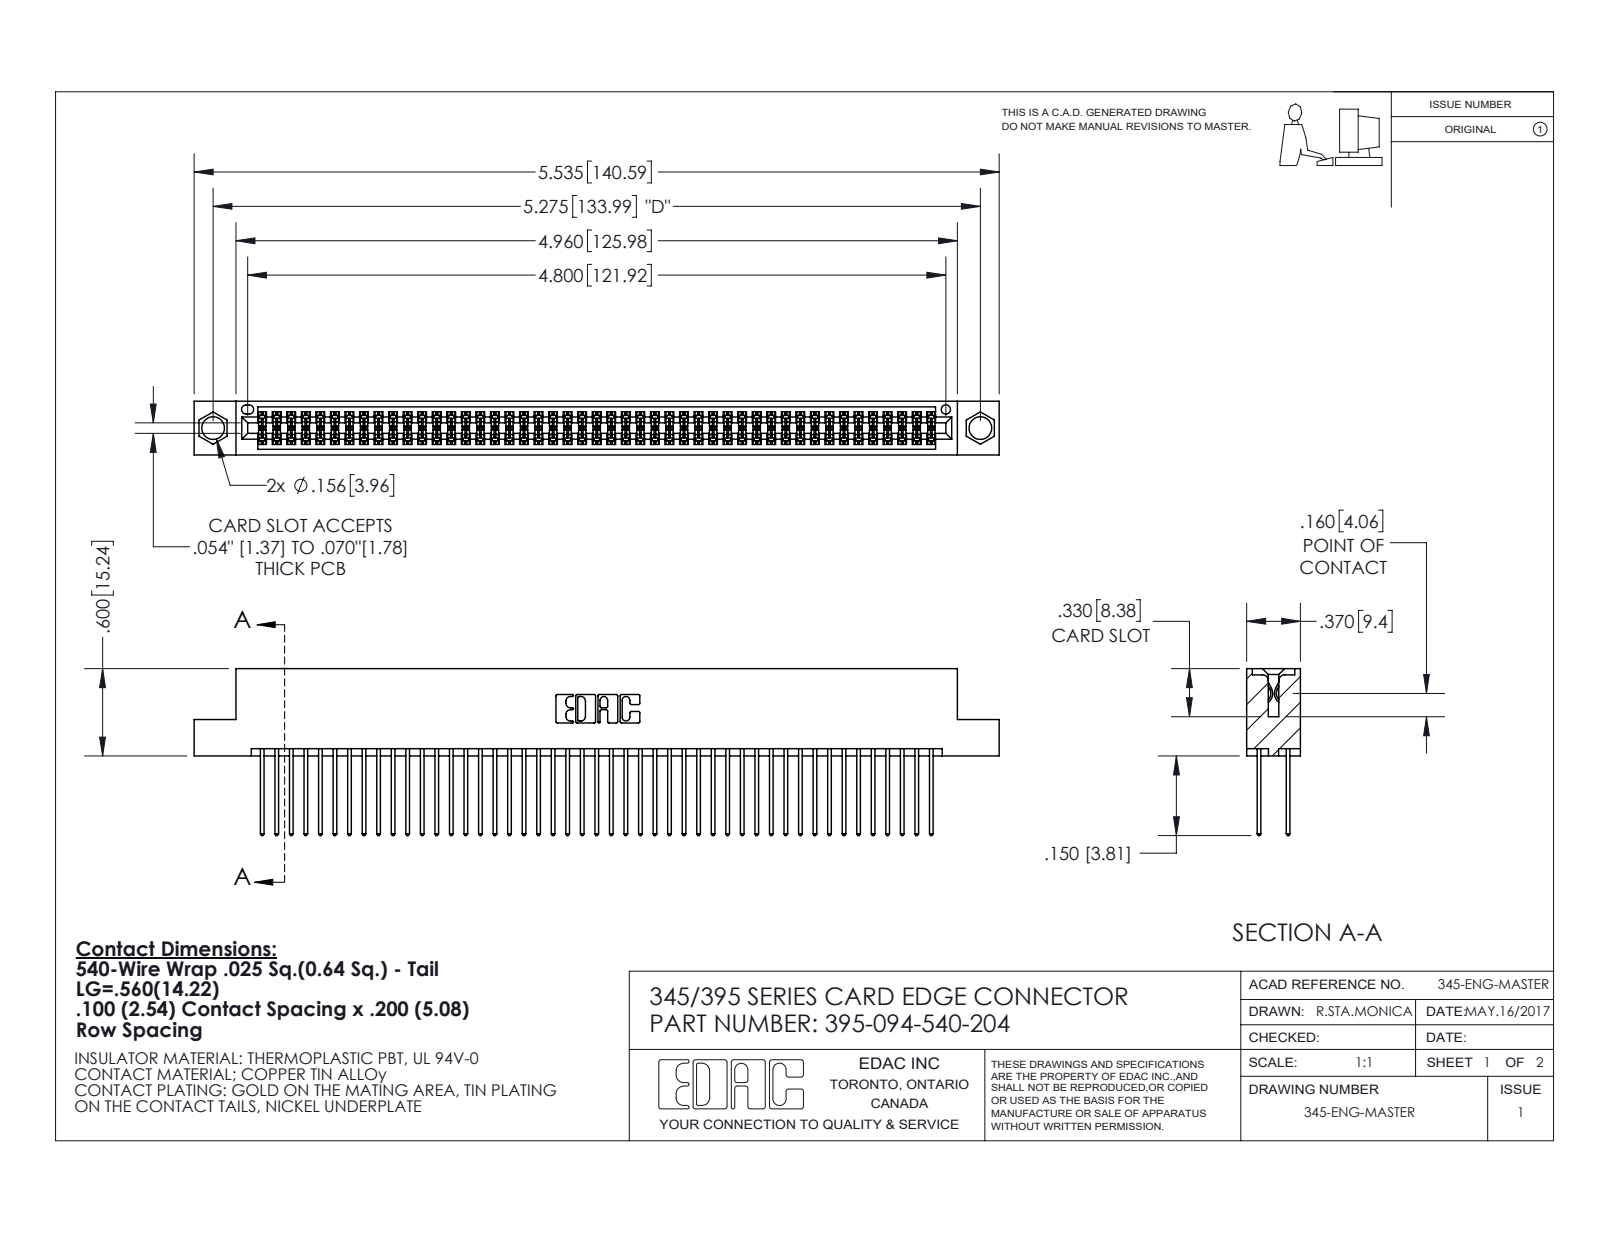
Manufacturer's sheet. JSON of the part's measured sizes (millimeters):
{"part_name": "395-094-540-204; 345 Part_Flush Mounting Lugs - 0.156 Dia-TI; 345-292-001_345-293-140", "step_written_by": "SolidWorks 2020 (CONFIG_CONTROL_DESIGN)", "units": "millimeters", "bodies": {"solids": 95, "faces": 4840, "planar": 3196, "cylindrical": 1644, "other": 0}, "overall_size": [140.6, 29.1, 9.4], "volume_mm3": 14000, "surface_area_mm2": 22230, "round_holes": [[4, 2], [1.6, 1]], "partial_cylinders_radius": [[0.2, 188], [0.3, 94], [0.3, 22], [0.2, 6], [0.8, 6], [0.7, 3], [0.4, 2], [0.5, 2]], "face_to_face_distances": [1.8, 7.6, 5.1, 2.5, 6.9, 0.6, 9.4, 5.7, 4.4, 3.8], "hole_center_spacings": [6.9, 128, 134]}
